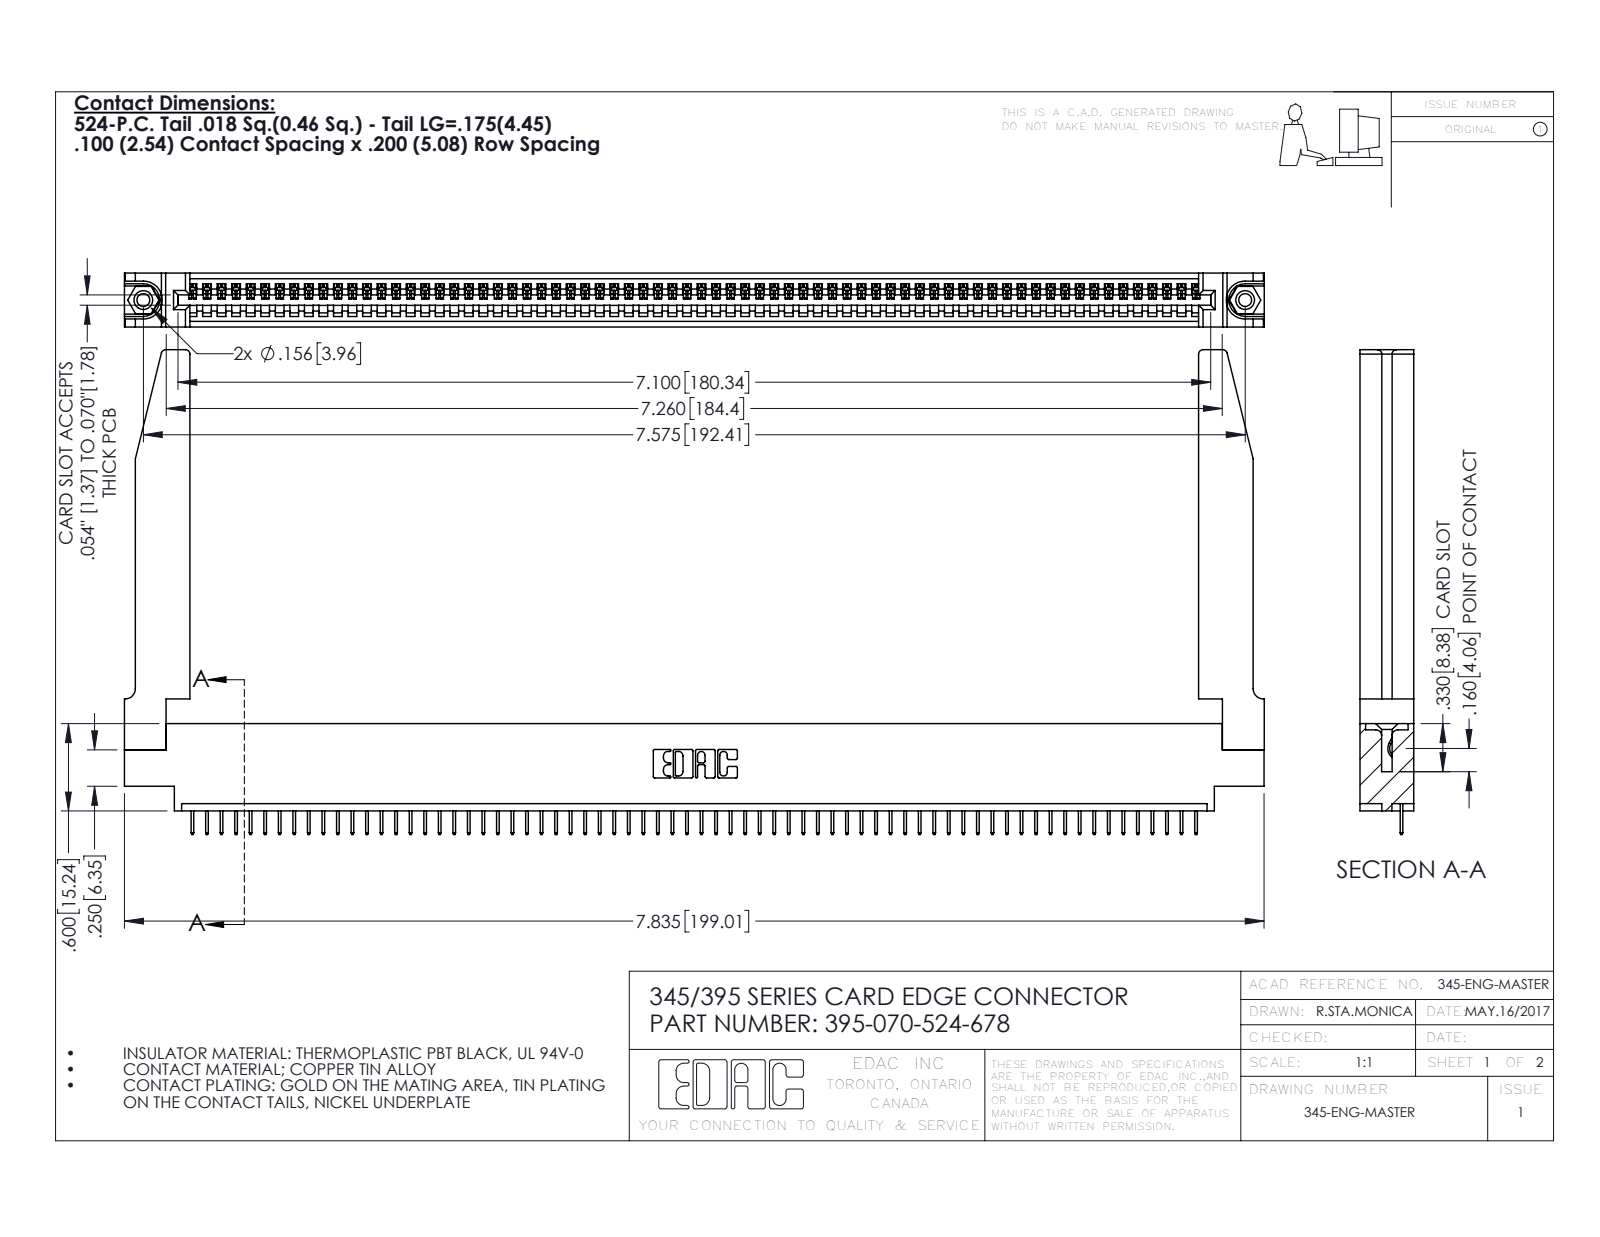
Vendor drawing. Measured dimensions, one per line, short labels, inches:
name: 345 Part_0.170 Offset - 0.156 Dia-TH; 345-220-078_345-220-078; 395-070-524-678; 345-292-001_345-293-124 (+1 more)
written by: SolidWorks 2016 (CONFIG_CONTROL_DESIGN)
unit: in
bodies: 75 solids, 4704 faces (3446 planar, 1206 cylindrical, 52 other)
size: 7.836 × 3.332 × 0.37
volume: 1.618 in³; area: 48.64 in²
holes: 2× ⌀0.089, 2× ⌀0.125, 2× ⌀0.156, 1× ⌀0.064
bosses: 2× ⌀0.155
rounds: 140× R0.006, 22× R0.01, 8× R0.03, 6× R0.007, 6× R0.031, 3× R0.026, 2× R0.031, 2× R0.04
face distances: 0.37, 0.072, 0.298, 0.098, 0.272, 0.025, 0.2, 0.225, 0.072, 0.175
hole spacings: 0.27, 7.339, 7.575
